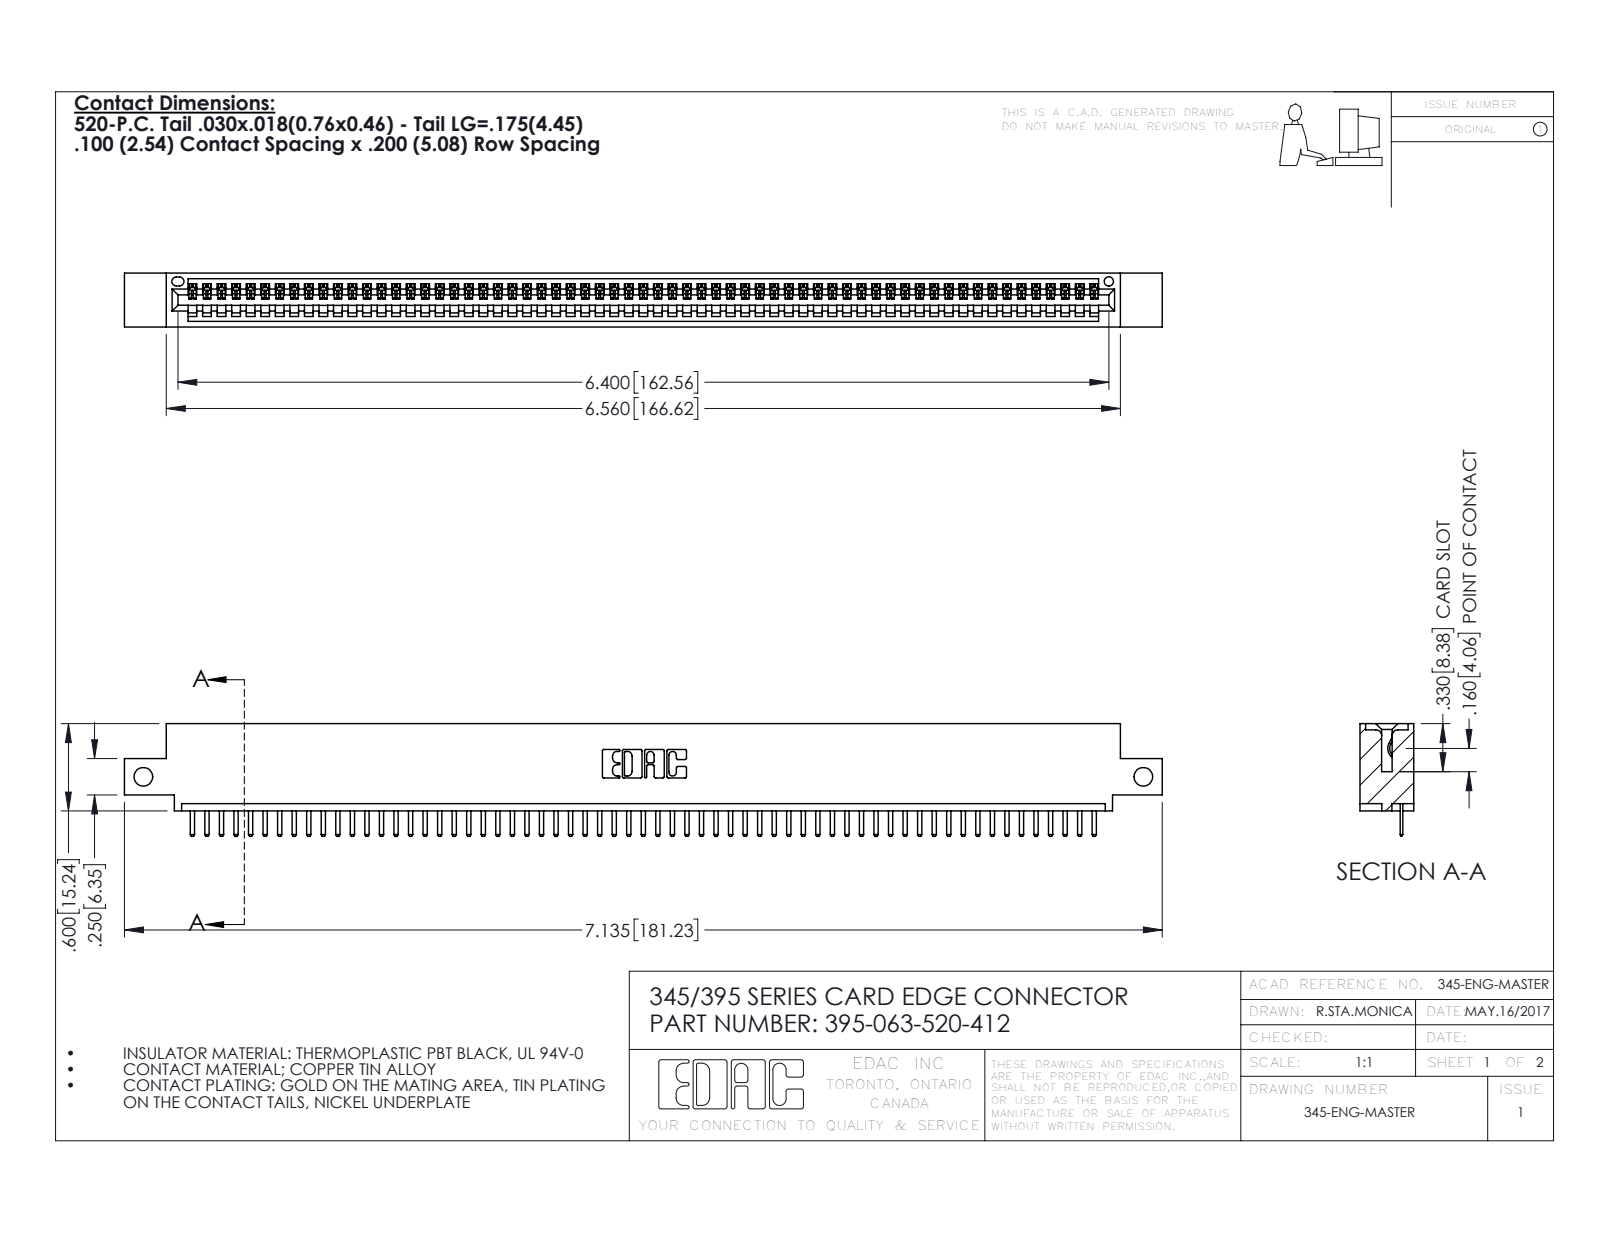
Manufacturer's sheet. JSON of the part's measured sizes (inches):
{"part_name": "345 Part_0.110 Offset - Side Mount; 395-063-520-412; 345-292-001_345-293-120", "step_written_by": "SolidWorks 2016 (CONFIG_CONTROL_DESIGN)", "units": "inches", "bodies": {"solids": 64, "faces": 4036, "planar": 2730, "cylindrical": 1306, "other": 0}, "overall_size": [7.135, 0.775, 0.37], "volume_in3": 1.04, "surface_area_in2": 34.54, "round_holes": [[0.128, 2], [0.064, 1]], "partial_cylinders_radius": [[0.01, 128], [0.006, 126], [0.01, 22], [0.007, 6], [0.031, 6], [0.026, 3], [0.031, 2], [0.04, 2]], "face_to_face_distances": [0.298, 0.072, 0.37, 0.2, 0.098, 0.272, 0.025, 0.225, 0.072, 0.149], "hole_center_spacings": [6.875]}
